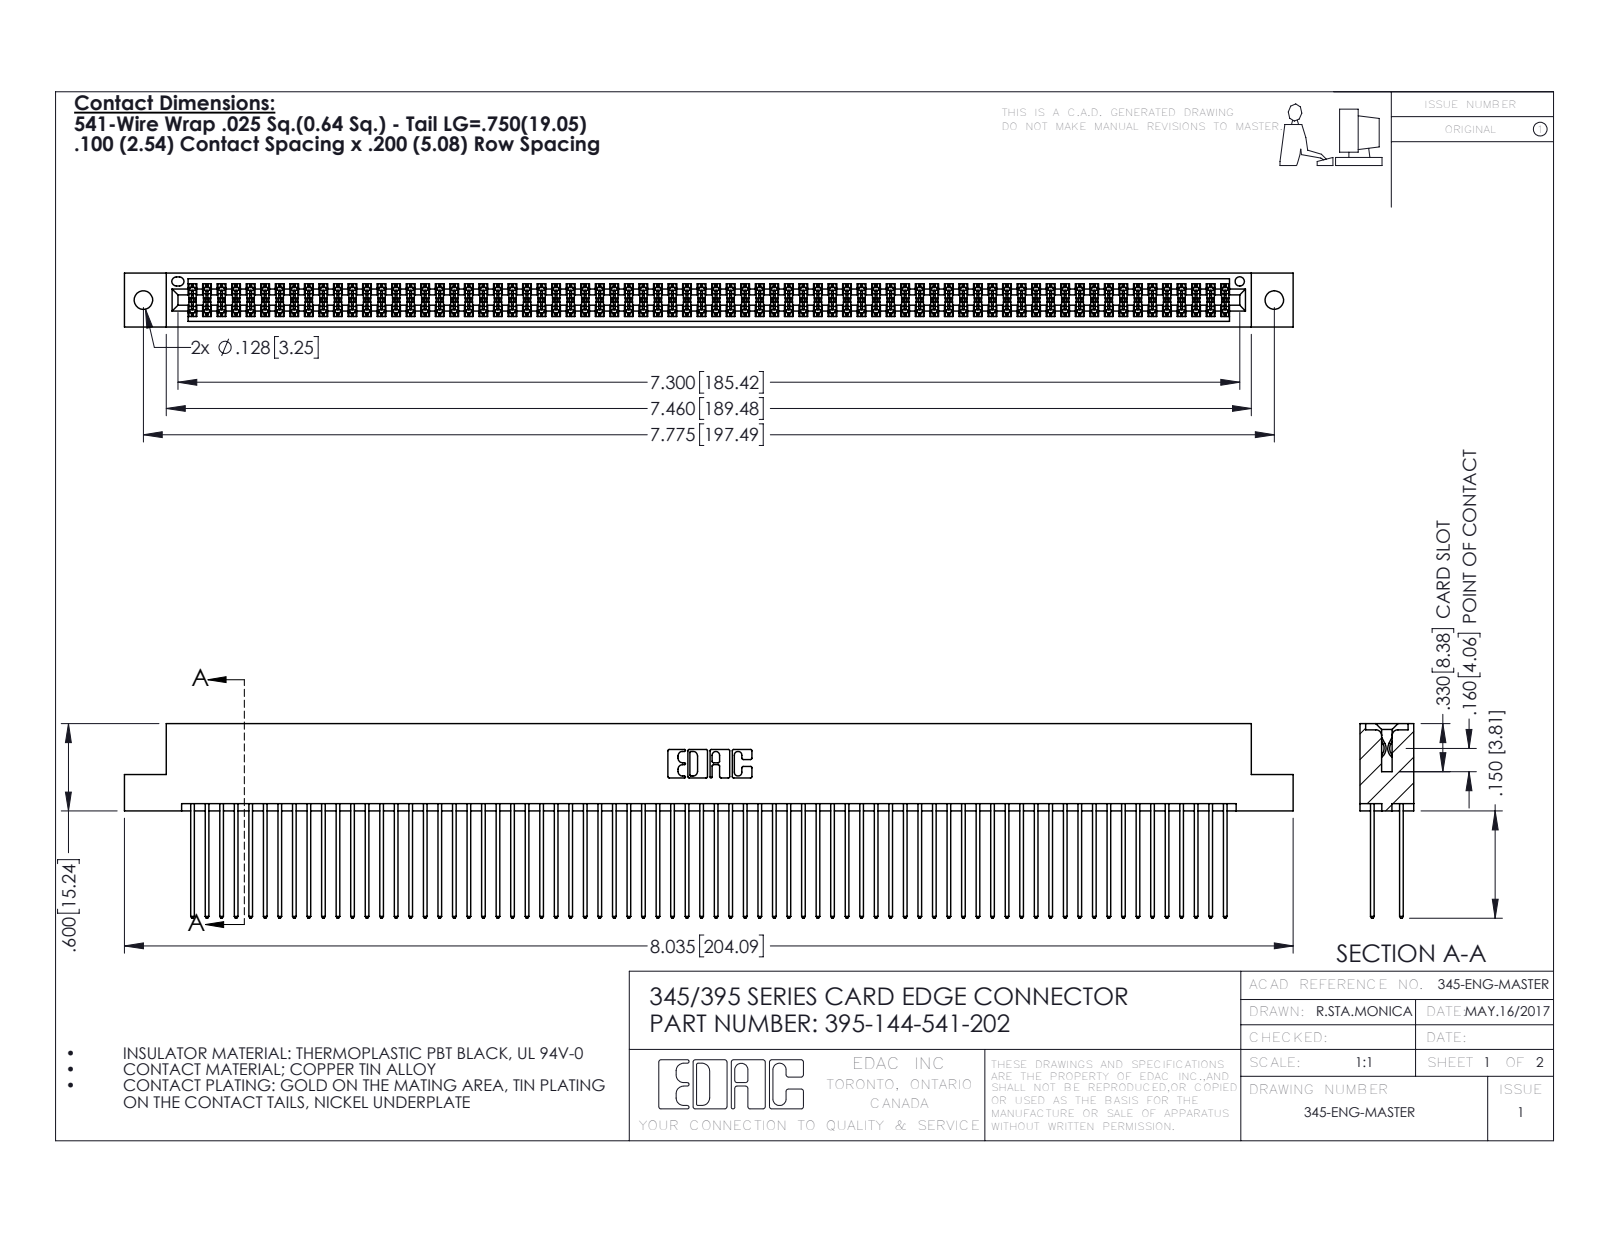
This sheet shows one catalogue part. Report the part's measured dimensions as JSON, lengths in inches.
{"part_name": "395-144-541-202; 345-292-001_345-293-141; 345 Part_Flush Mounting Lugs - 0.128 Dia", "step_written_by": "SolidWorks 2016 (CONFIG_CONTROL_DESIGN)", "units": "inches", "bodies": {"solids": 145, "faces": 7326, "planar": 4832, "cylindrical": 2494, "other": 0}, "overall_size": [8.035, 1.337, 0.37], "volume_in3": 1.275, "surface_area_in2": 54.37, "round_holes": [[0.128, 2], [0.064, 1]], "partial_cylinders_radius": [[0.006, 216], [0.01, 144], [0.01, 22], [0.007, 6], [0.031, 6], [0.026, 3], [0.014, 2], [0.019, 2]], "face_to_face_distances": [0.298, 0.072, 0.2, 0.098, 0.272, 0.025, 0.225, 0.37, 0.175, 0.149], "hole_center_spacings": [0.27, 7.539, 7.775]}
